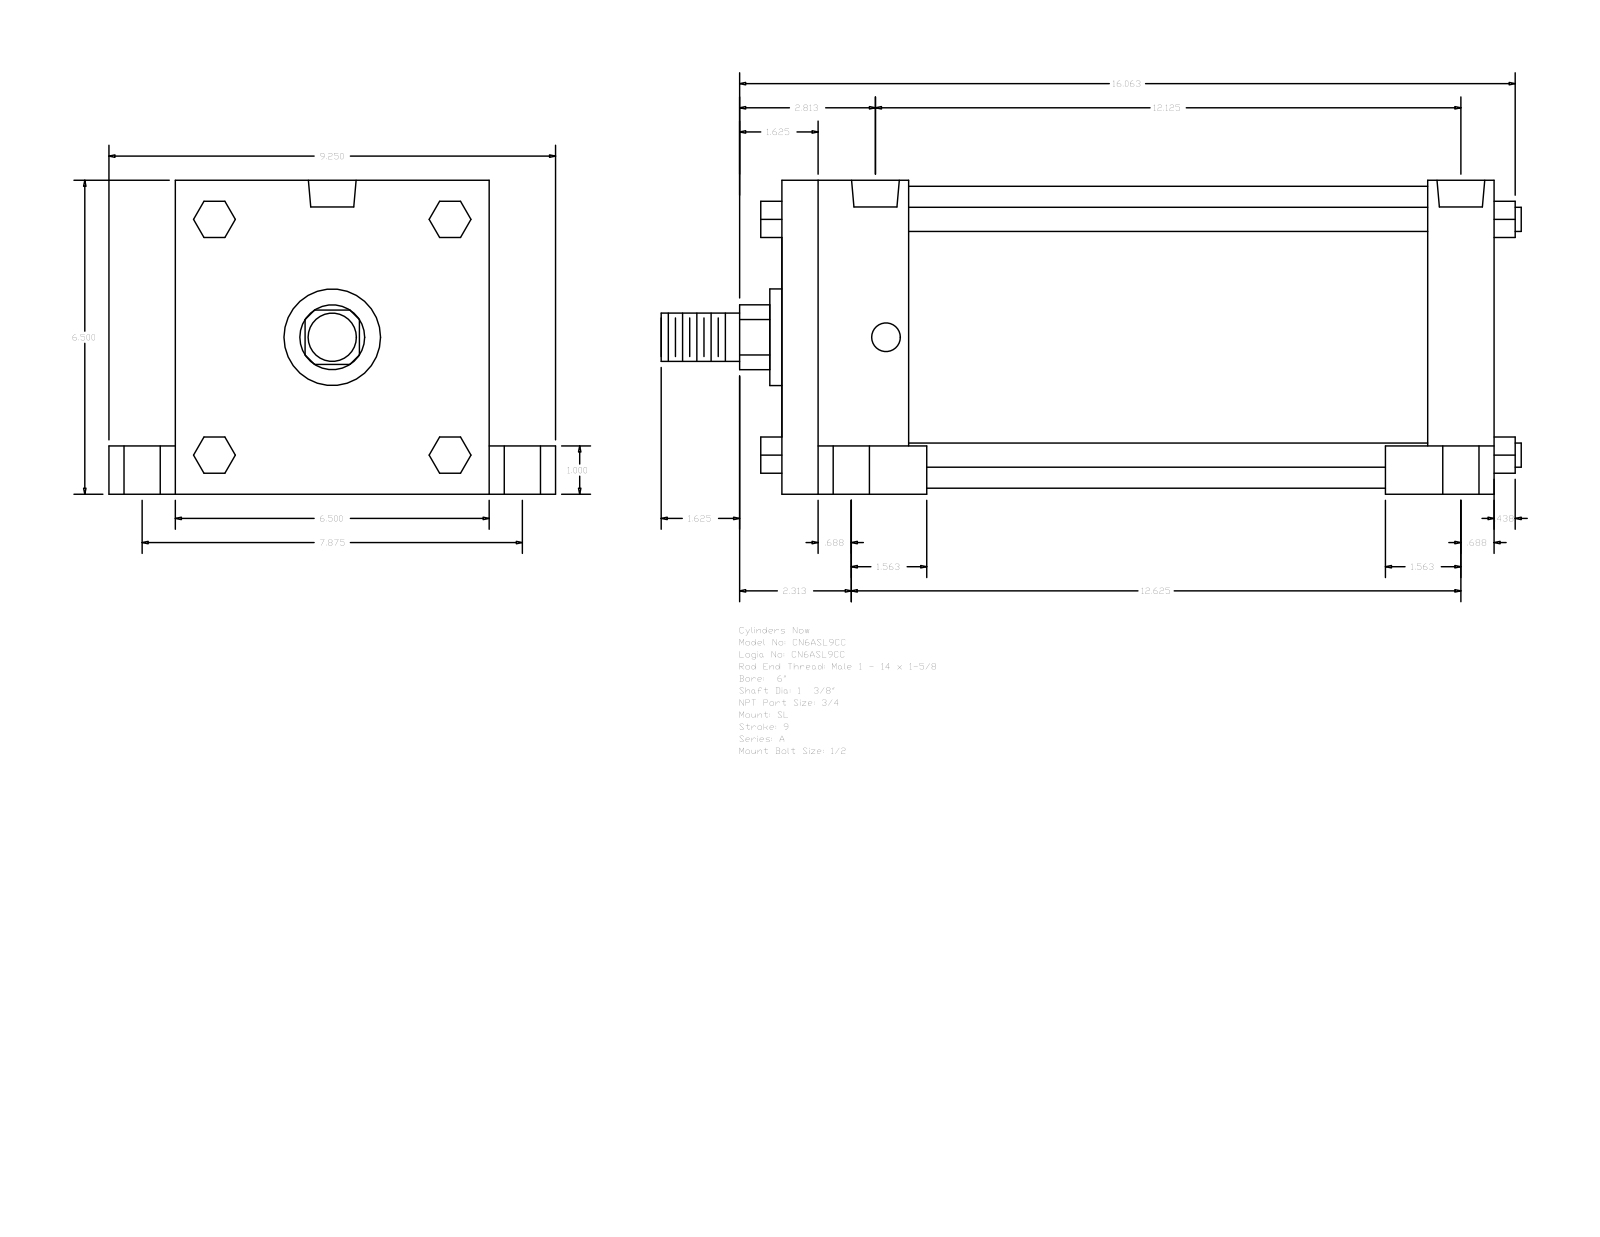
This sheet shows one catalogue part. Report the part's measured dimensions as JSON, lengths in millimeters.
{"part_name": "A_SL__0600_1.375", "step_written_by": "GSSL Pune (CONFIG_CONTROL_DESIGN)", "units": "millimeters", "bodies": {"solids": 0, "faces": 150, "planar": 114, "cylindrical": 36, "other": 0}, "overall_size": [452.44, 234.95, 165.1], "round_holes": [[15.08, 4], [19.05, 4], [25.4, 4], [25.12, 2]], "round_bosses_or_shafts": [[12.7, 4], [158.75, 1], [50.8, 1], [34.92, 1], [25.4, 1]], "partial_cylinders_radius": [[17.06, 1]], "face_to_face_distances": [165.1, 374.65, 66.67, 307.98, 339.72, 273.05, 34.93, 25.4, 139.7, 34.92], "hole_center_spacings": [5.56, 100.01, 100.16, 100.81, 101.66, 200.02, 296.85, 302.41]}
